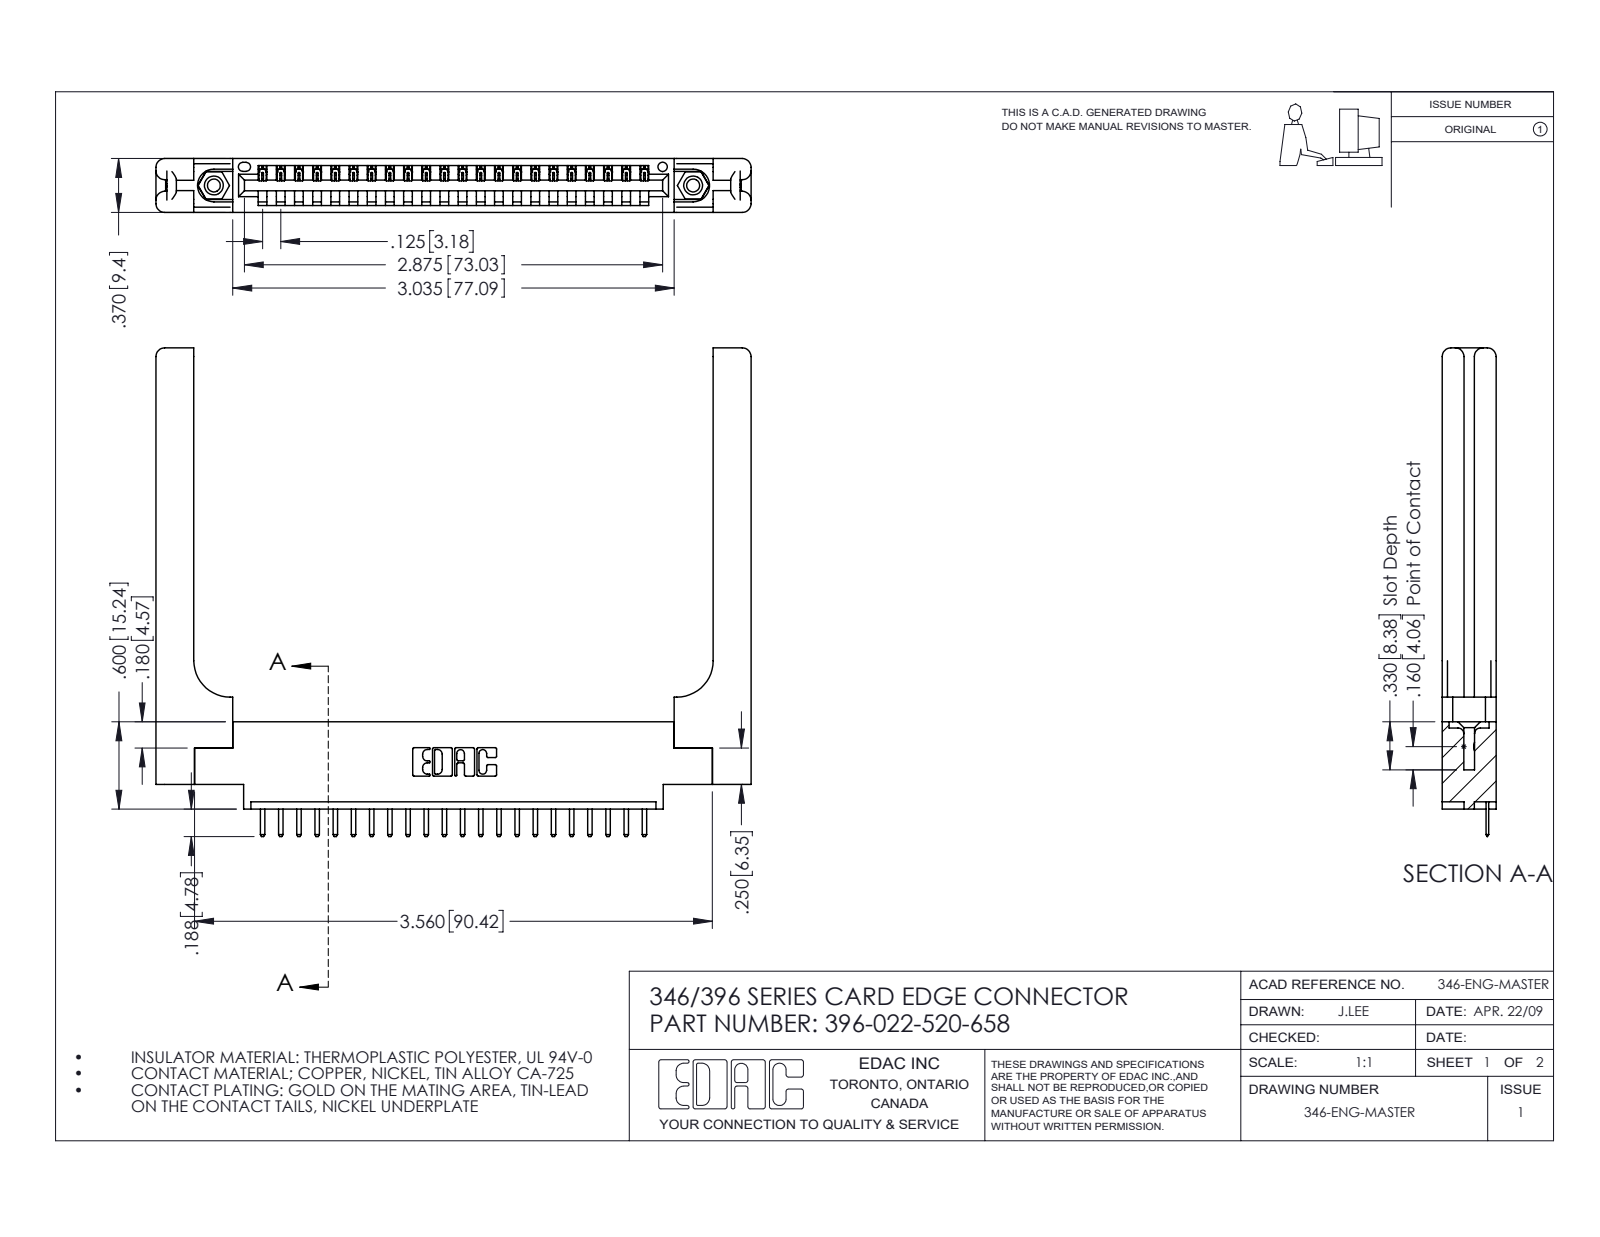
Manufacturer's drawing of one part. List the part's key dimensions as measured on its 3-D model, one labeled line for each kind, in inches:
Part name (STEP PRODUCT): 346-220-058_345-220-058; 346 Part_0.170 Offset - 0.156 Dia-TH; 345-250-001_345-250-001-102; 345-292-001_345-293-120 (+1 more)
STEP written by: SolidWorks 2016 (CONFIG_CONTROL_DESIGN)
Units: inches
Bodies: 27 solids, 1746 faces (1152 planar, 534 cylindrical, 60 other)
Overall size (bounding box): 4.091 × 3.358 × 0.37
Volume: 1.044 in³ · Surface area: 26.18 in²
Round holes (diameter × count): ⌀0.089 ×2, ⌀0.125 ×2, ⌀0.156 ×2, ⌀0.064 ×1
Round bosses / shafts (diameter × count): ⌀0.155 ×2
Partial cylindrical surfaces — rounded edges, fillets, slot ends (radius × count): R0.01 ×46, R0.006 ×44, R0.01 ×22, R0.06 ×16, R0.007 ×6, R0.031 ×6, R0.026 ×3, R0.03 ×2
Main face-to-face distances: 0.37, 0.072, 0.15, 0.148, 0.048, 0.322, 0.25, 0.102, 0.22, 0.173
Hole centre spacings: 0.246, 3.087, 3.295
